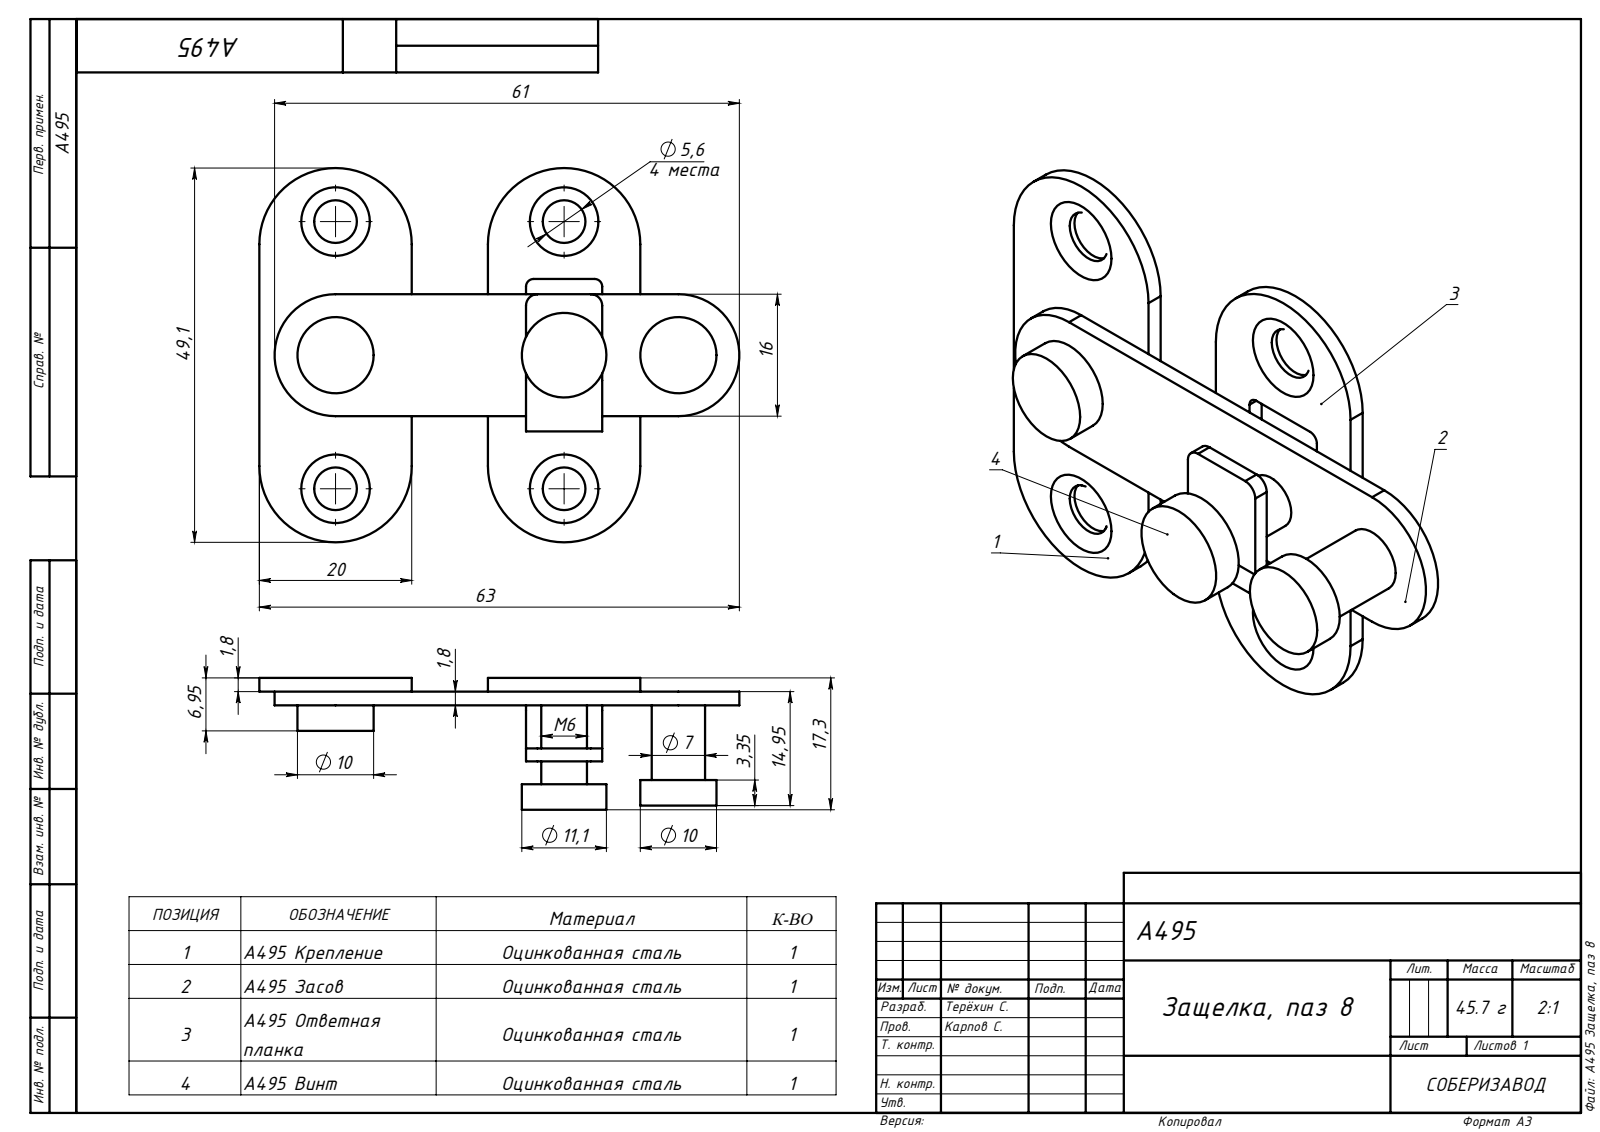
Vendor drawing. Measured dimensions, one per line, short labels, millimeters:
name: A495 Ответная планка_00; A495 Винт_00; A495 Защелка, паз 8; A495 Крепление_00 (+1 more)
written by: SolidWorks 2021 (AUTOMOTIVE_DESIGN)
unit: mm
bodies: 4 solids, 83 faces (33 planar, 42 cylindrical, 8 other)
size: 63 × 49.1 × 17.3
volume: 6 184 mm³; area: 7 365 mm²
holes: 4× ⌀5.6, 1× ⌀5, 1× ⌀6.5
bosses: 2× ⌀10, 1× ⌀11.1, 1× ⌀7, 1× ⌀6
rounds: 5× R1.5, 4× R1, 4× R10, 2× R8, 1× R5, 1× R6.7
face distances: 1.8, 3.6, 3.35, 15, 10.35, 10, 20, 9.8, 0.55, 30
hole spacings: 17.52, 34.74, 30, 35.04, 46.13
